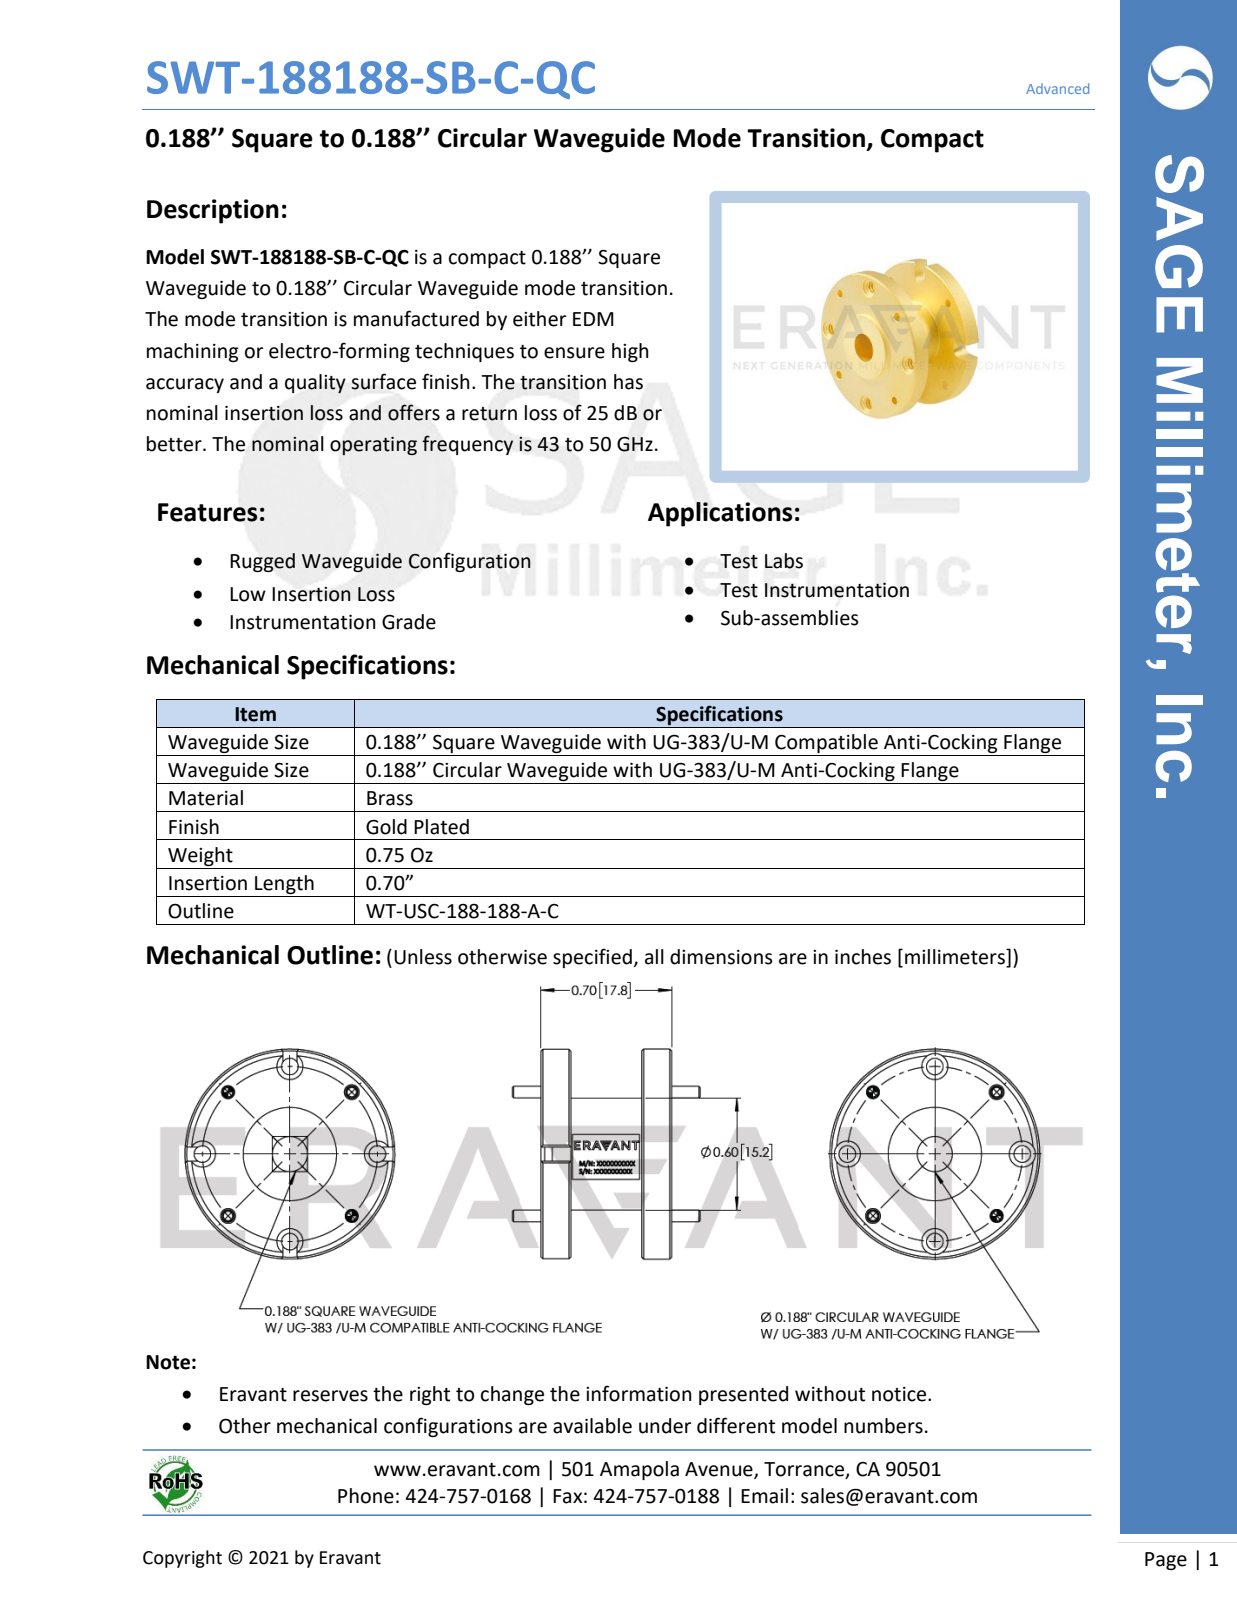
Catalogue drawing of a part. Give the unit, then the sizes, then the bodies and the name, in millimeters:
Units: millimetres
Overall size (bounding box): 28.6 × 28.6 × 25.5
Round holes (diameter × count): ⌀1.5 ×4, ⌀1.7 ×4, ⌀2.3 ×4, ⌀3.6 ×4, ⌀26.8 ×1
Round bosses / shafts (diameter × count): ⌀1.6 ×4, ⌀28.6 ×1, ⌀28.6 ×1, ⌀15.2 ×1, ⌀12.7 ×1
Main face-to-face distances: 3.6, 13.2, 9.7, 16.8, 0.5, 4.1, 13.7, 17.3, 17.8, 1.5
Hole centre spacings: 9.1, 11.9, 16.8, 22, 23.8
Volume: 6 310 mm³ · Surface area: 3 870 mm²
Bodies: 5 solids, 175 faces (45 planar, 78 cylindrical, 52 other)
Part name (STEP PRODUCT): WT-USC-188-188-A-C, Defeatured
STEP written by: SolidWorks 2021 (AUTOMOTIVE_DESIGN)
